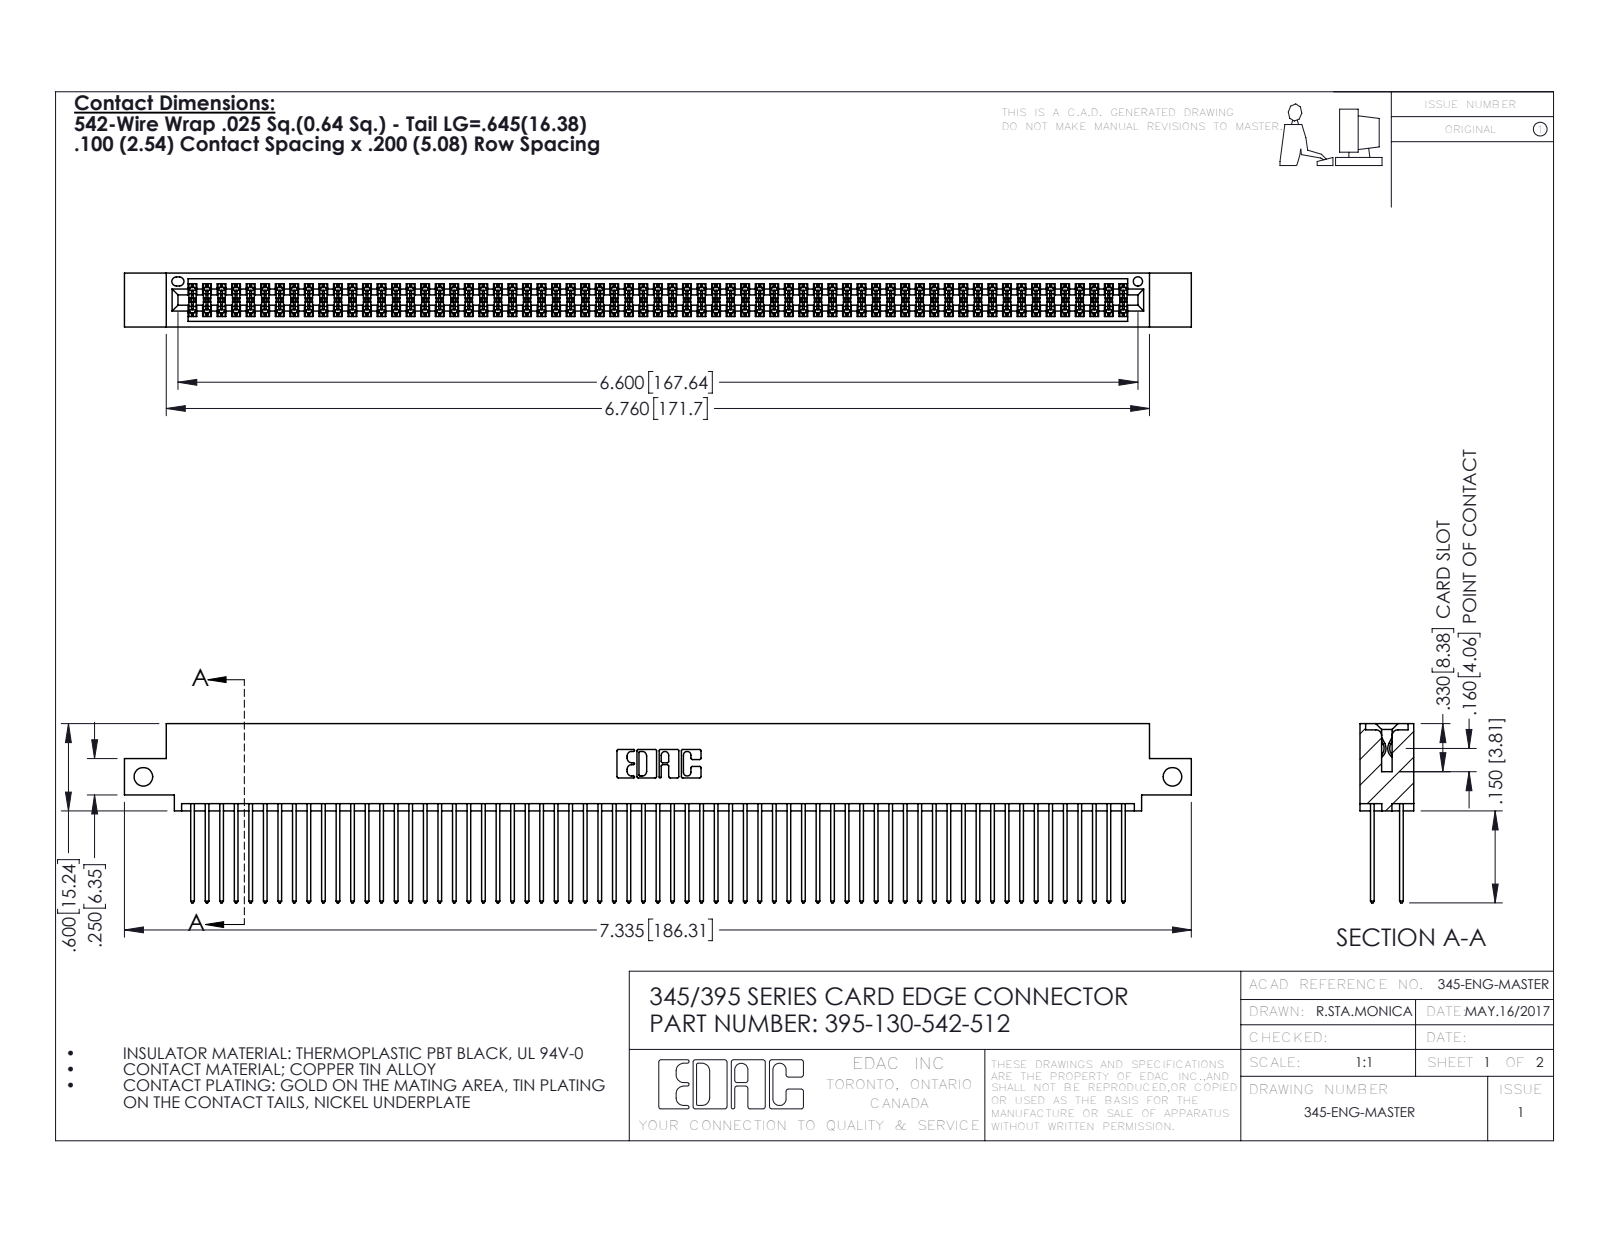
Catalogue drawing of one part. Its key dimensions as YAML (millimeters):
part_name: "395-130-542-512; 345 Part_0.110 Offset - Side Mount; 345-292-001_345-293-142"
step_written_by: "SolidWorks 2016 (CONFIG_CONTROL_DESIGN)"
units: millimeters
bodies: {solids: 131, faces: 6630, planar: 4374, cylindrical: 2256, other: 0}
overall_size: [186.3, 31.3, 9.4]
volume: 18760
surface_area: 30960
round_holes:
  - {diameter: 3.3, count: 2}
  - {diameter: 1.6, count: 1}
partial_cylinders:
  - {radius: 0.2, count: 195}
  - {radius: 0.3, count: 130}
  - {radius: 0.3, count: 22}
  - {radius: 0.2, count: 6}
  - {radius: 0.8, count: 6}
  - {radius: 0.7, count: 3}
  - {radius: 0.4, count: 2}
  - {radius: 0.5, count: 2}
face_to_face_distances: [1.8, 7.6, 5.1, 2.5, 6.9, 0.6, 5.7, 9.4, 4.4, 3.8]
hole_center_spacings: [179.7]
